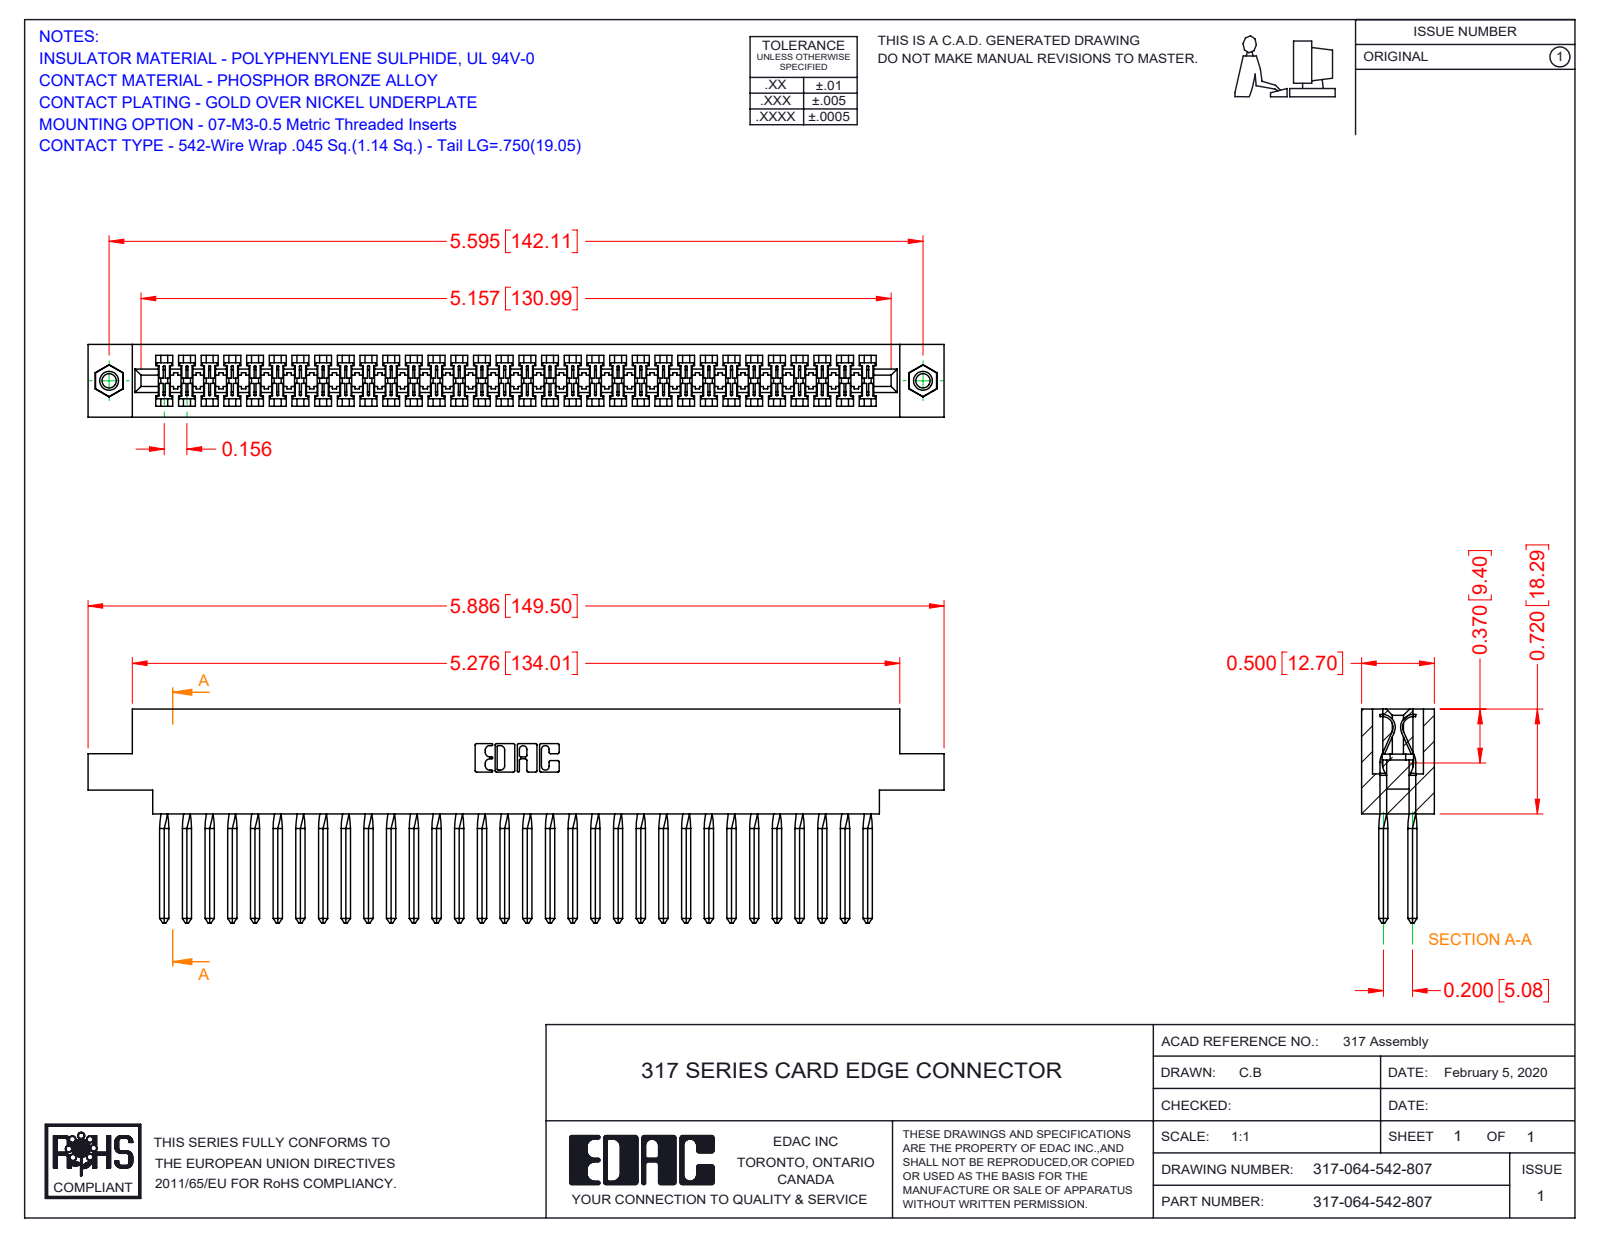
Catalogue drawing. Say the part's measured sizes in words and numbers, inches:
The part is named "317 Part_.156 Dia - TI; 317-064-542-807; 345-250-001_345-250-005-103; 317-290-003_542". Its 3-D file was written by "SolidWorks 2016 (CONFIG_CONTROL_DESIGN)". It is 67 solids with 3810 faces: 3034 planar, 504 cylindrical and 272 other. Overall it measures 5.886 by 1.47 by 0.5 inches. Its volume is 1.474 cubic inches and its surface area 51.62 square inches. Round holes: 2 of diameter 0.098, 2 of diameter 0.125, 2 of diameter 0.156. Round bosses or shafts: 2 of diameter 0.155. Partial cylindrical surfaces (rounded edges, fillets, slot ends): 128 of radius 0.006, 22 of radius 0.01, 6 of radius 0.007, 6 of radius 0.031, 3 of radius 0.026, 2 of radius 0.074, 2 of radius 0.089, 2 of radius 0.1. The main face-to-face distances are 0.5, 0.075, 0.425, 0.35, 0.2, 0.116, 0.11, 0.046, 0.128, 0.372. The hole center spacings are 5.595.
